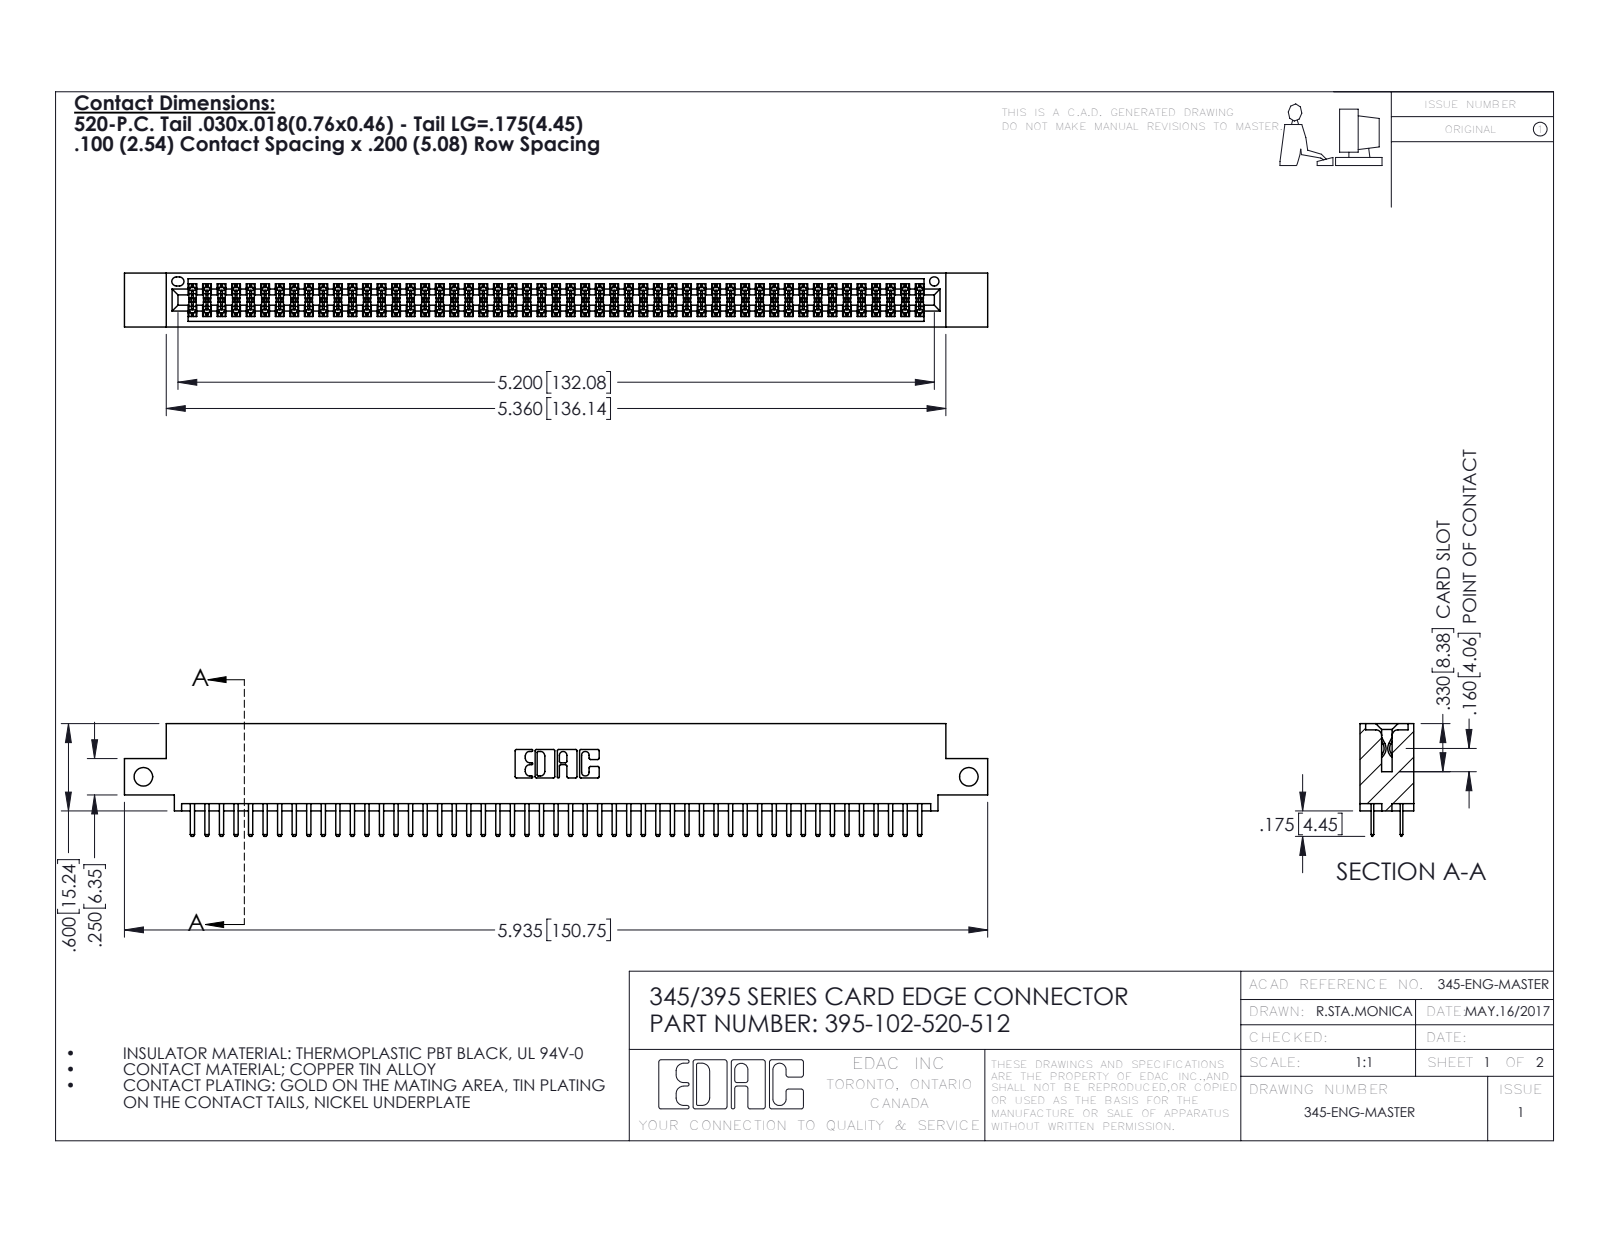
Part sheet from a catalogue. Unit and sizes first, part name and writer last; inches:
Units: inches
Overall size (bounding box): 5.935 × 0.775 × 0.37
Round holes (diameter × count): ⌀0.128 ×2, ⌀0.064 ×1
Partial cylindrical surfaces — rounded edges, fillets, slot ends (radius × count): R0.006 ×153, R0.01 ×106, R0.01 ×22, R0.007 ×6, R0.031 ×6, R0.026 ×3, R0.014 ×2, R0.019 ×2
Main face-to-face distances: 0.298, 0.072, 0.2, 0.37, 0.098, 0.272, 0.025, 0.225, 0.022, 0.072
Hole centre spacings: 5.675
Volume: 0.886 in³ · Surface area: 33.33 in²
Bodies: 103 solids, 5638 faces (3654 planar, 1984 cylindrical, 0 other)
Part name (STEP PRODUCT): 345 Part_0.110 Offset - Side Mount; 345-292-001_345-293-120; 395-102-520-512
STEP written by: SolidWorks 2016 (CONFIG_CONTROL_DESIGN)
